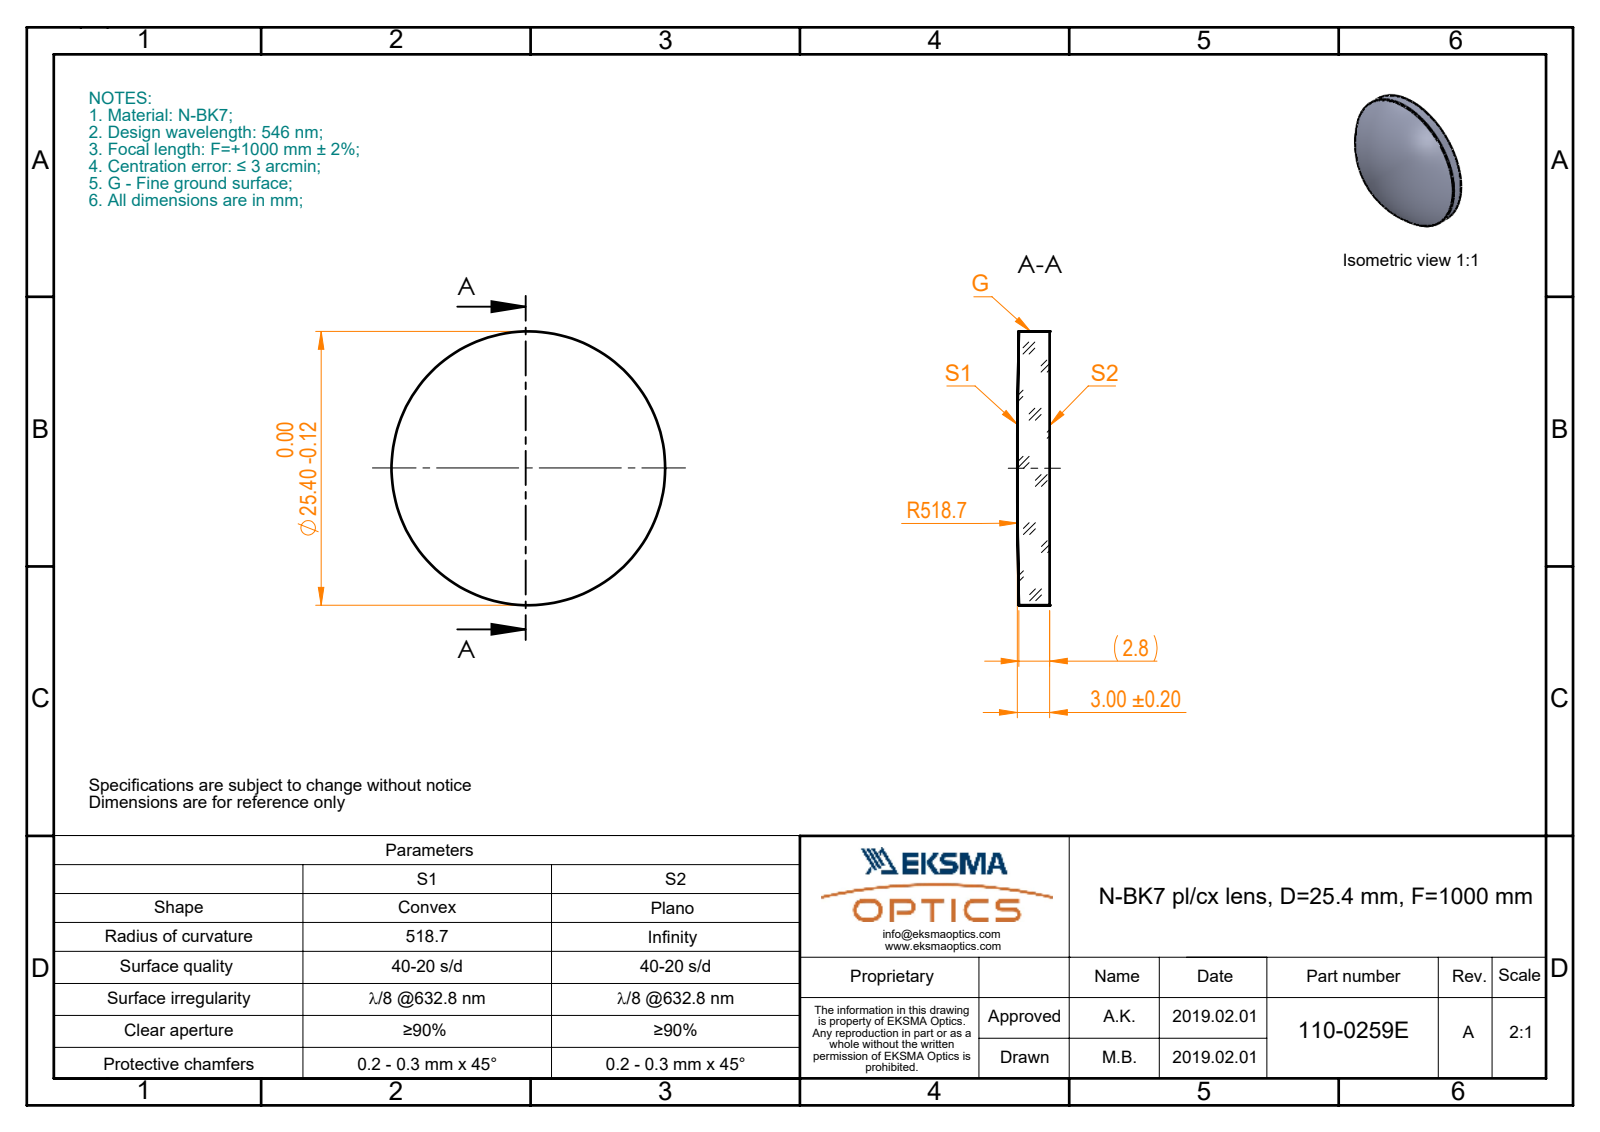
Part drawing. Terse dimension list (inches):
name: 110-0259E BK7 pl-cx 25.4 F1000
written by: SolidWorks 2017 (CONFIG_CONTROL_DESIGN)
unit: in
bodies: 1 solid, 5 faces (1 planar, 2 cylindrical, 2 other)
size: 1 × 1 × 0.118
volume: 0.09 in³; area: 1.922 in²
bosses: 1× ⌀1
